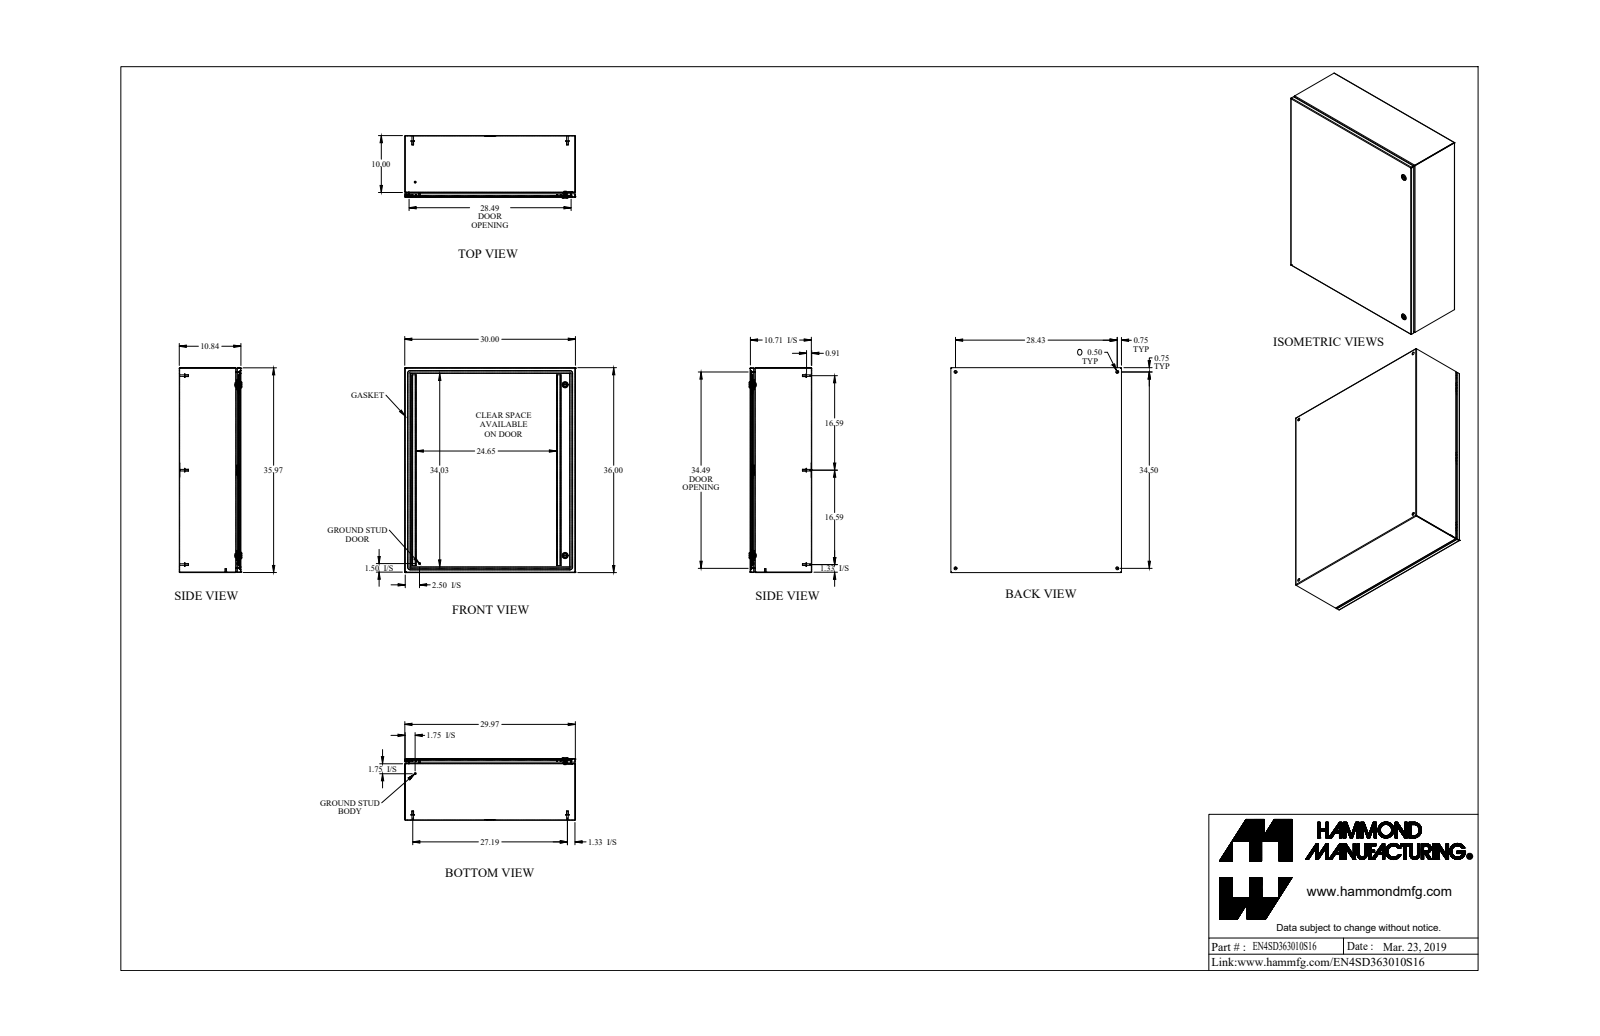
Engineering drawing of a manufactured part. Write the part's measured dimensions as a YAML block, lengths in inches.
part_name: "EN4SD363010S16"
step_written_by: "SolidWorks 2019 (AUTOMOTIVE_DESIGN)"
units: inches
bodies: {solids: 35, faces: 958, planar: 458, cylindrical: 312, other: 188}
overall_size: [36, 30, 11.002]
volume: 286.6
surface_area: 8035
round_holes:
  - {diameter: 0.5, count: 6}
  - {diameter: 0.197, count: 2}
  - {diameter: 0.387, count: 2}
  - {diameter: 0.63, count: 2}
  - {diameter: 0.768, count: 2}
  - {diameter: 0.172, count: 1}
  - {diameter: 0.24, count: 1}
  - {diameter: 0.242, count: 1}
round_bosses_or_shafts:
  - {diameter: 0.625, count: 8}
  - {diameter: 0.313, count: 8}
  - {diameter: 0.275, count: 6}
  - {diameter: 1.1, count: 2}
  - {diameter: 0.785, count: 2}
  - {diameter: 0.525, count: 2}
  - {diameter: 0.25, count: 2}
  - {diameter: 0.236, count: 2}
partial_cylinders:
  - {radius: 0.036, count: 20}
  - {radius: 0.108, count: 20}
  - {radius: 0.25, count: 16}
  - {radius: 0.01, count: 12}
  - {radius: 0.048, count: 12}
  - {radius: 0.006, count: 6}
  - {radius: 0.062, count: 6}
  - {radius: 0.125, count: 4}
face_to_face_distances: [0.072, 10.77, 10.698, 10.842, 29.928, 35.928, 29.856, 30, 35.856, 36]
hole_center_spacings: [27.531, 28.428, 34.5, 44.704, 2.457, 2.458, 30, 32.265]
